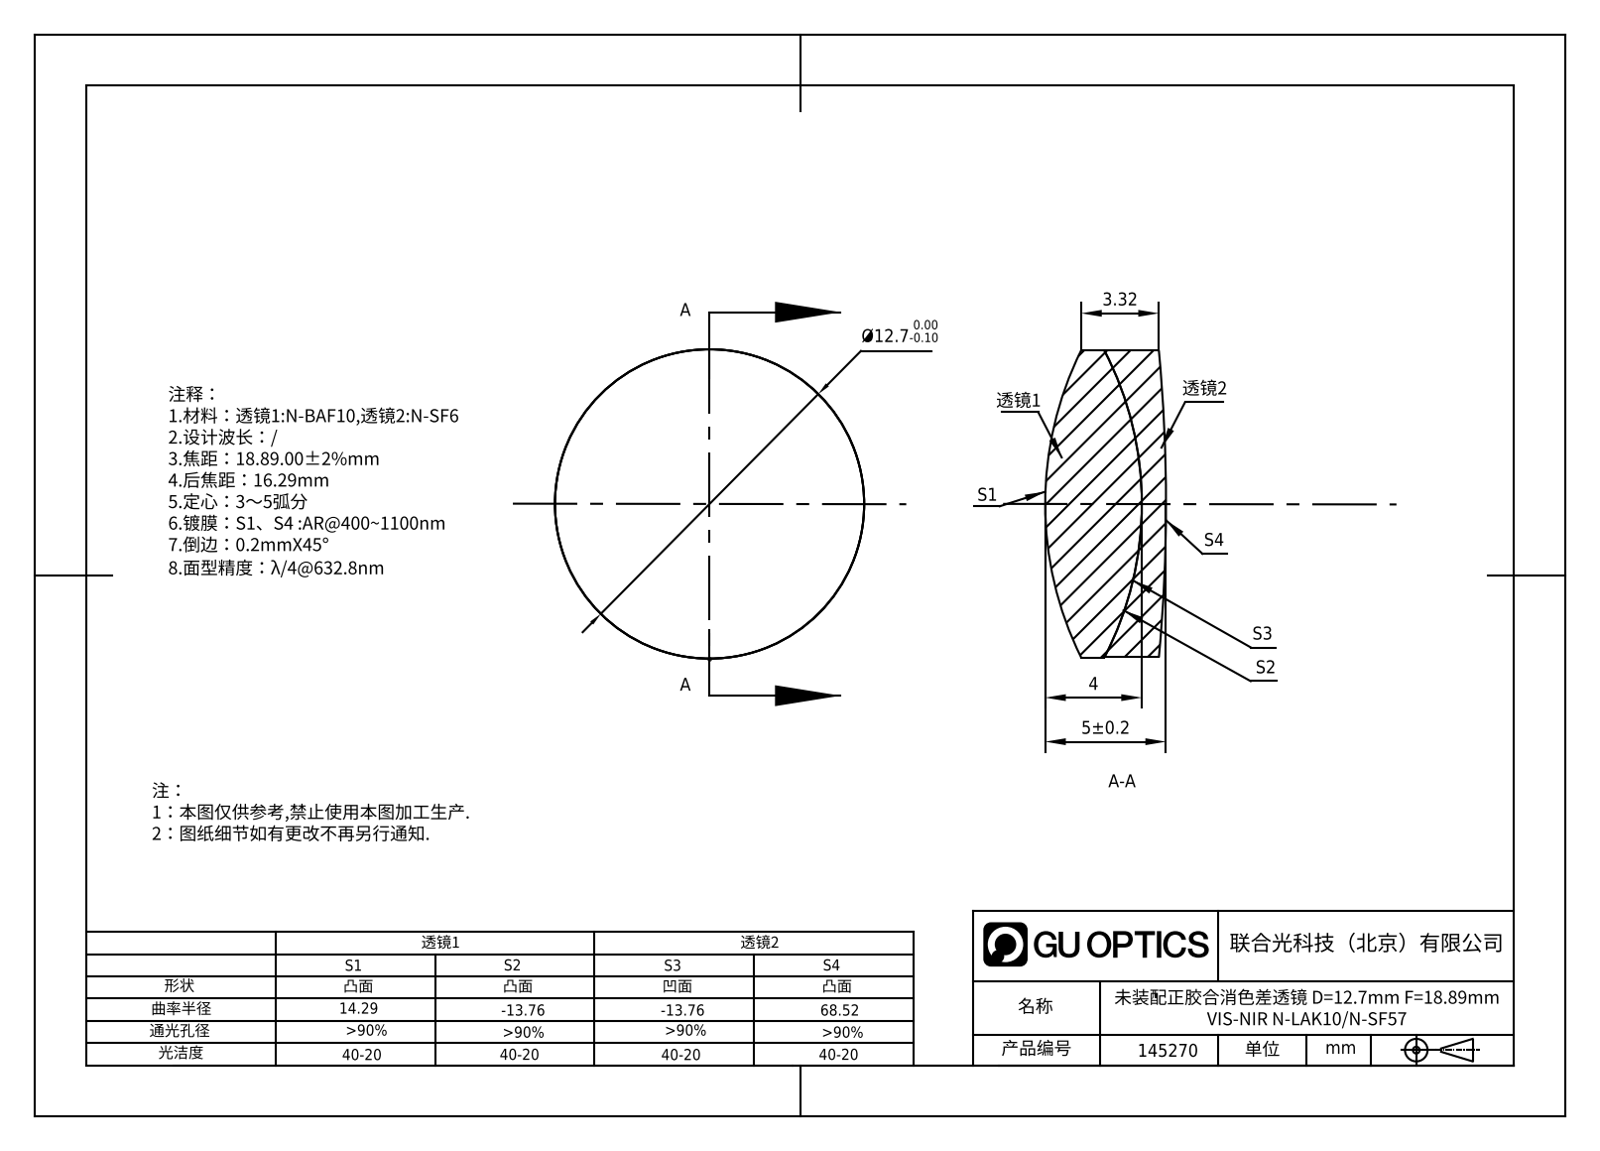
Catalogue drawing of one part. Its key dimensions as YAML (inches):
part_name: "145270b; 145270a; 装配体1"
step_written_by: "SolidWorks 2020 (CONFIG_CONTROL_DESIGN)"
units: inches
bodies: {solids: 2, faces: 12, planar: 0, cylindrical: 4, other: 8}
overall_size: [0.5, 0.5, 0.197]
volume: 0.032
surface_area: 1.02
round_bosses_or_shafts:
  - {diameter: 0.5, count: 1}
  - {diameter: 0.5, count: 1}
